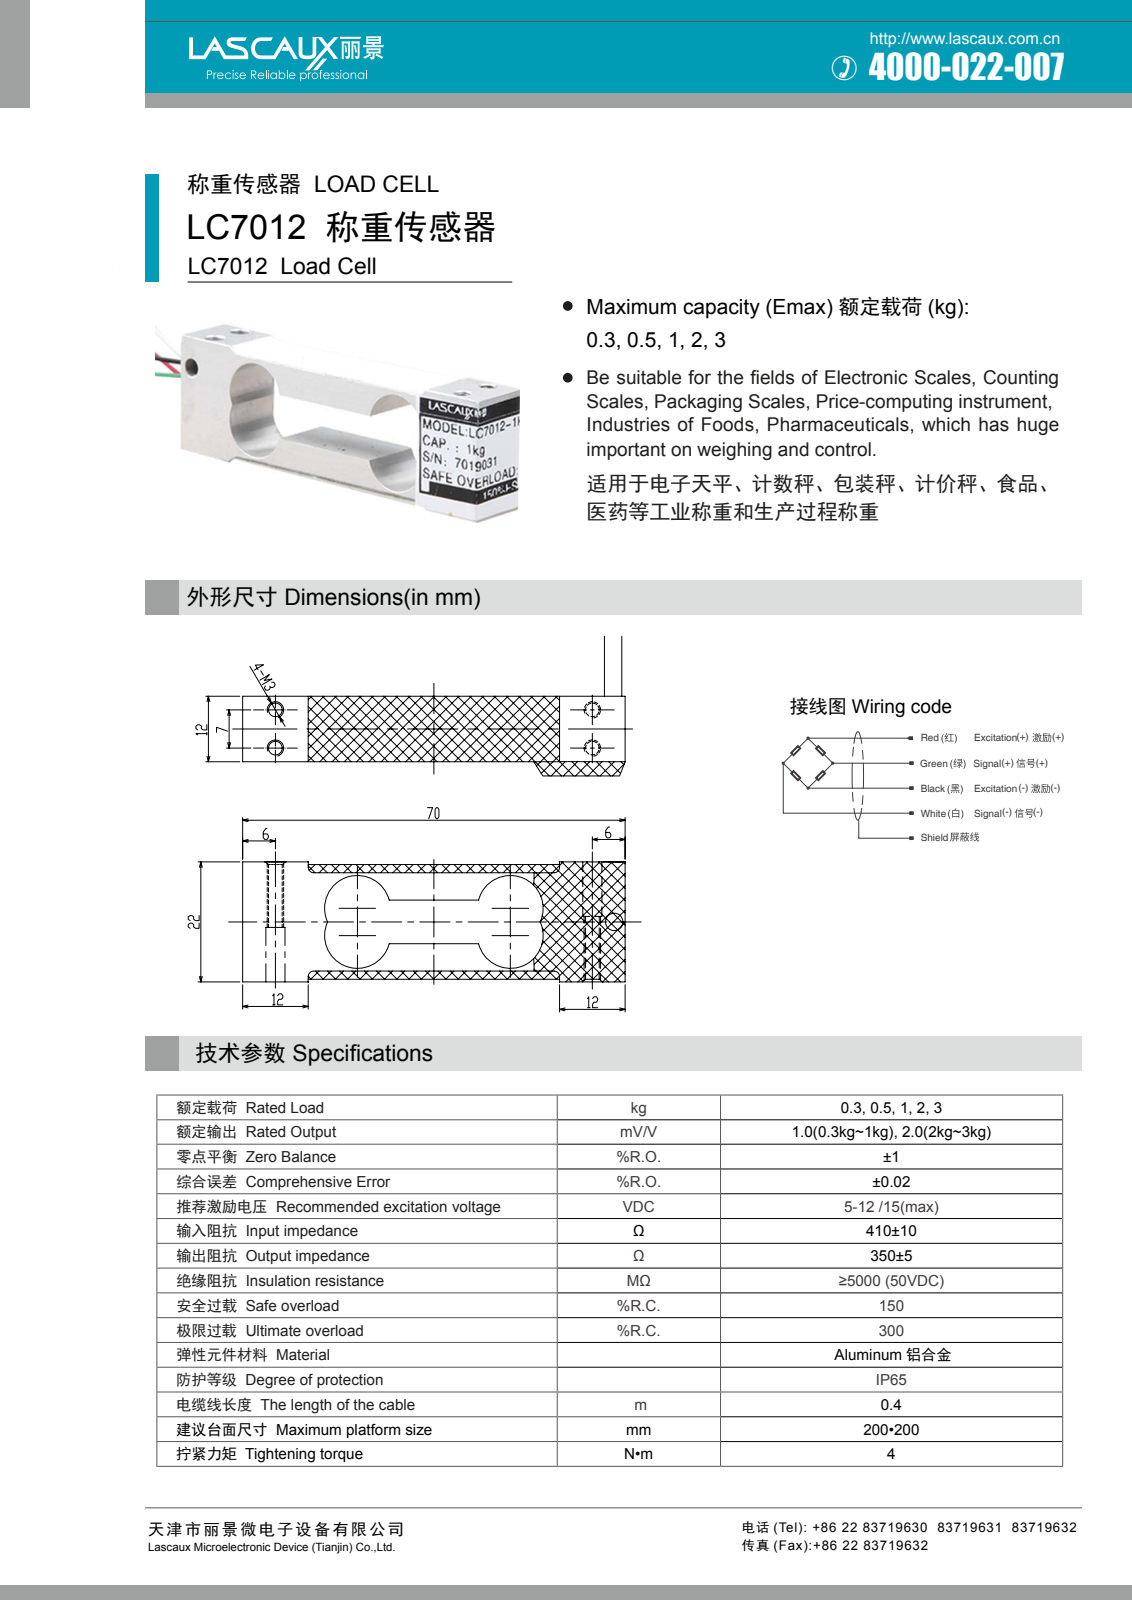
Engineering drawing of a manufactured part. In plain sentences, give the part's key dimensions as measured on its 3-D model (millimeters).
The part is named "传感器LC7012". Its 3-D file was written by "SolidWorks 2016 (CONFIG_CONTROL_DESIGN)". It is 1 solid with 42 faces: 17 planar, 25 cylindrical and 0 other. Overall it measures 75 by 22 by 14 millimeters. Its volume is 12 020 cubic millimeters and its surface area 6 484 square millimeters. Round holes: 4 of diameter 2.5. Round bosses or shafts: 1 of diameter 2. Partial cylindrical surfaces (rounded edges, fillets, slot ends): 8 of radius 1, 4 of radius 4. The main face-to-face distances are 12, 2, 5.88, 12.12, 7.88, 14.12, 20, 18, 6.24, 22. The hole center spacings are 7, 58, 58.42.
